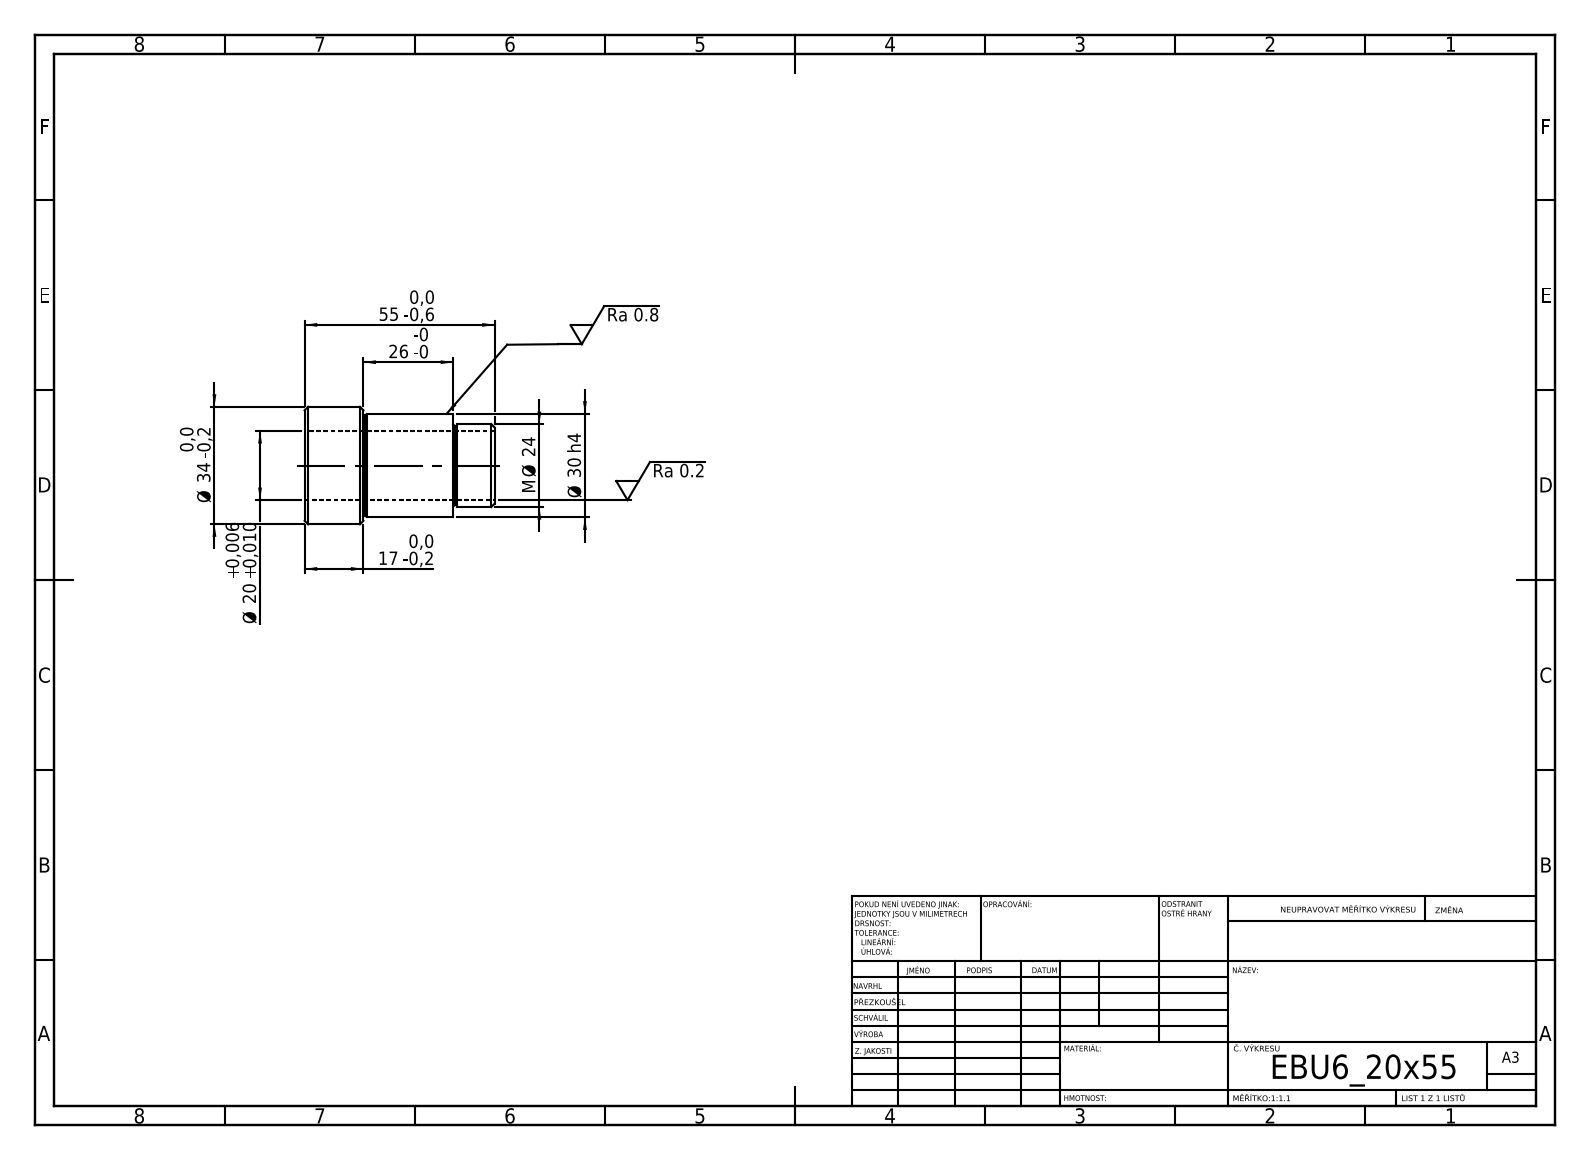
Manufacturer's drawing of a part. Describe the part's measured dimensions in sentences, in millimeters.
Its 3-D file was written by "SolidWorks 2019 (CONFIG_CONTROL_DESIGN)". It is 1 solid with 27 faces: 5 planar, 12 cylindrical and 10 other. Overall it measures 55 by 34 by 34 millimeters. Its volume is 21 747 cubic millimeters and its surface area 9 767 square millimeters. Round holes: 1 of diameter 20. Round bosses or shafts: 1 of diameter 34, 1 of diameter 30, 1 of diameter 29, 1 of diameter 24, 1 of diameter 23. The main face-to-face distances are 43, 26, 17, 12, 38, 55, 11, 1, 27, 44.
